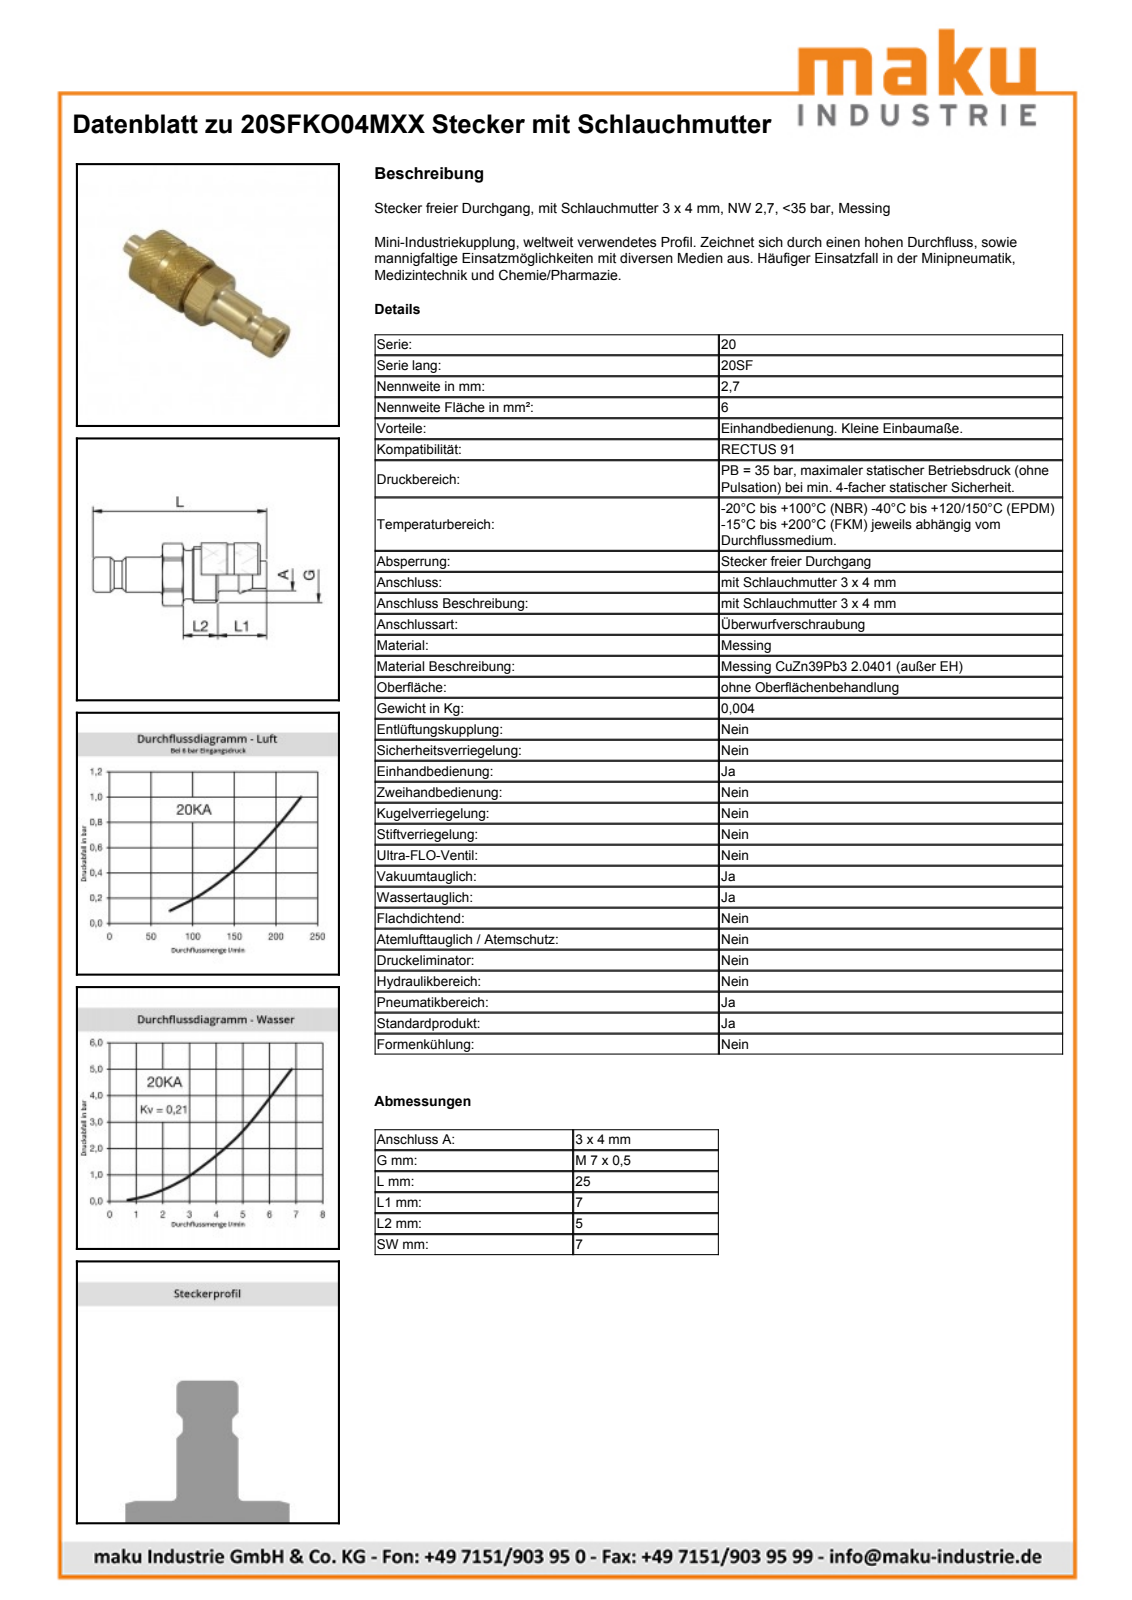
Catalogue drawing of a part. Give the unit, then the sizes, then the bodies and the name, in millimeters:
Units: millimetres
Overall size (bounding box): 25 × 8.1 × 8.1
Round holes (diameter × count): ⌀1.95 ×1, ⌀2.7 ×1, ⌀4.25 ×1, ⌀6.5 ×1
Round bosses / shafts (diameter × count): ⌀8.1 ×1, ⌀7.7 ×1, ⌀7 ×1, ⌀6.2 ×1, ⌀6 ×1, ⌀5 ×1, ⌀3.95 ×1, ⌀3.5 ×1
Partial cylindrical surfaces — rounded edges, fillets, slot ends (radius × count): R3.95 ×1
Main face-to-face distances: 7, 8.5, 5.61, 2.89, 13.61, 8, 5.11, 3.75, 4.75, 23.61
Volume: 619 mm³ · Surface area: 1 107 mm²
Bodies: 2 solids, 68 faces (15 planar, 21 cylindrical, 32 other)
Part name (STEP PRODUCT): D109602; D109601; D109384
STEP written by: Autodesk Inventor 2013 (AUTOMOTIVE_DESIGN)
